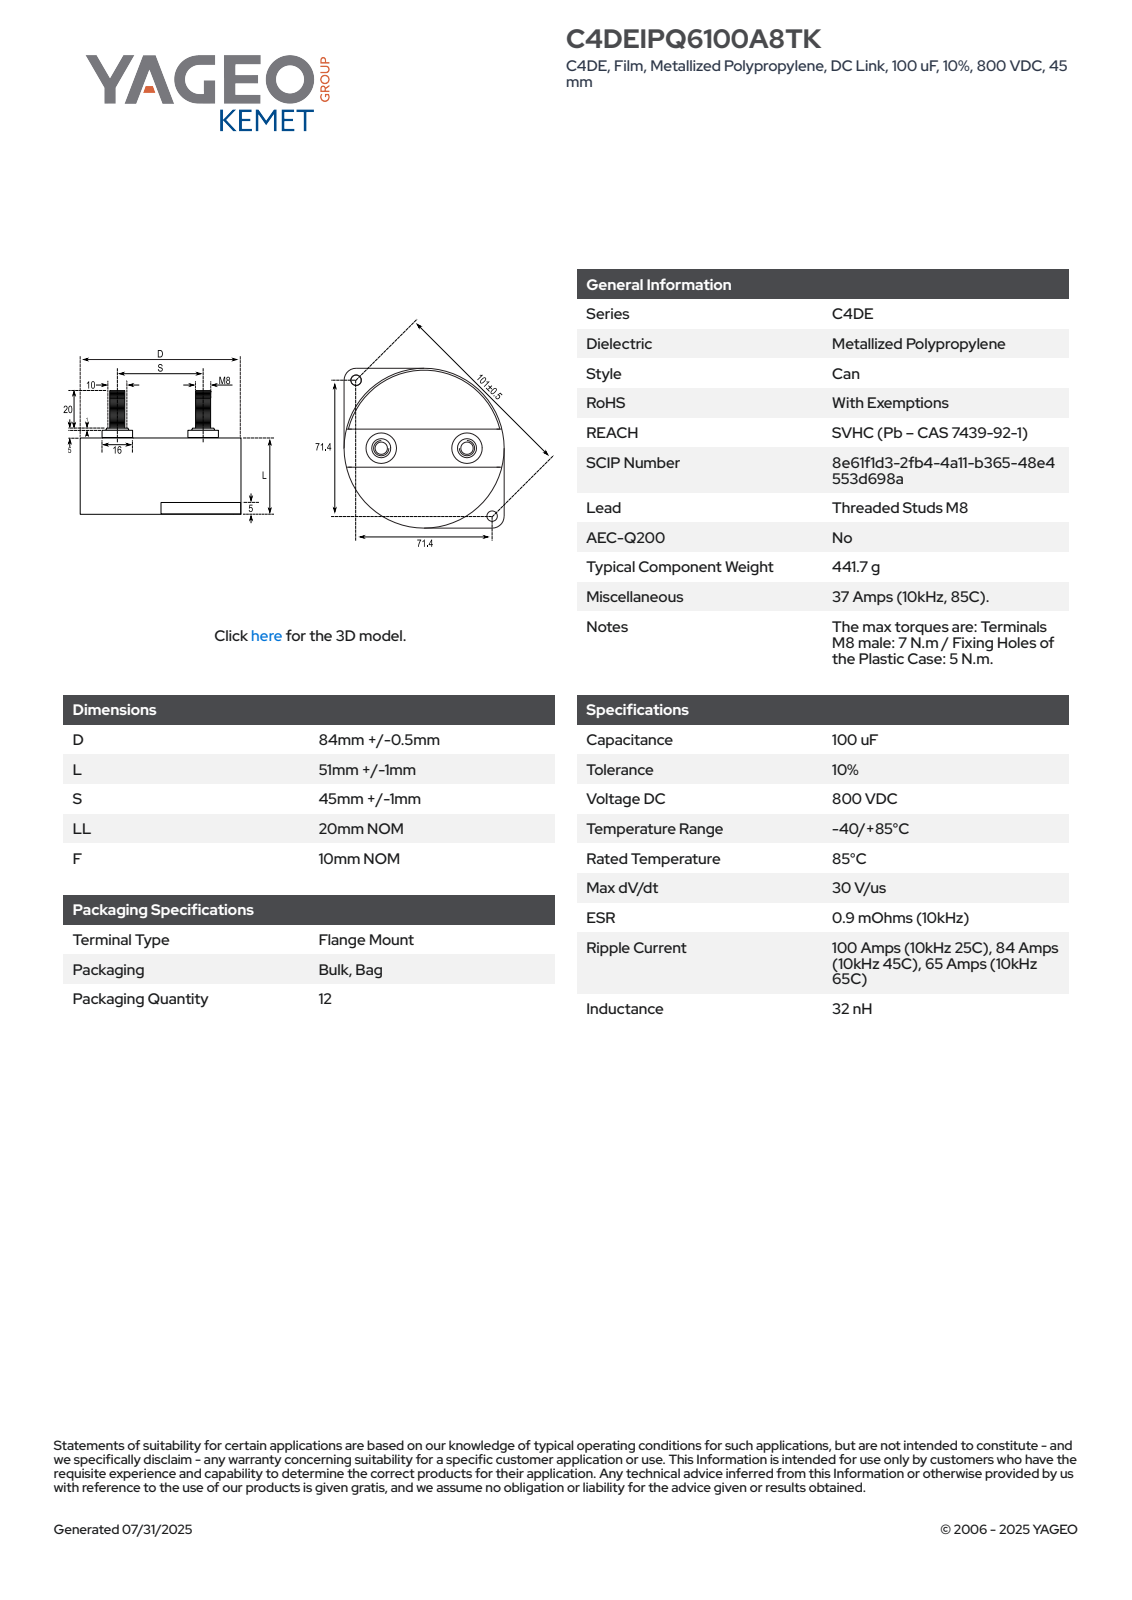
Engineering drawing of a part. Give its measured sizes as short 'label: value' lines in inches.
name: CFP_C44DE_84X51_D84.5L53S46LL20
written by: SolidWorks 2014 (AUTOMOTIVE_DESIGN)
unit: in
bodies: 1 solid, 103 faces (37 planar, 31 cylindrical, 35 other)
size: 3.327 × 3.327 × 3.11
volume: 18.6 in³; area: 44.18 in²
holes: 2× ⌀0.217
bosses: 2× ⌀0.63, 2× ⌀0.394, 2× ⌀0.315, 1× ⌀3.327, 1× ⌀3.15
rounds: 2× R0.394, 1× R1.664
face distances: 2.087, 0.197, 1.89, 3.327, 2.283, 3.11, 2.913, 1.024, 0.827, 2.323
hole spacings: 3.996
